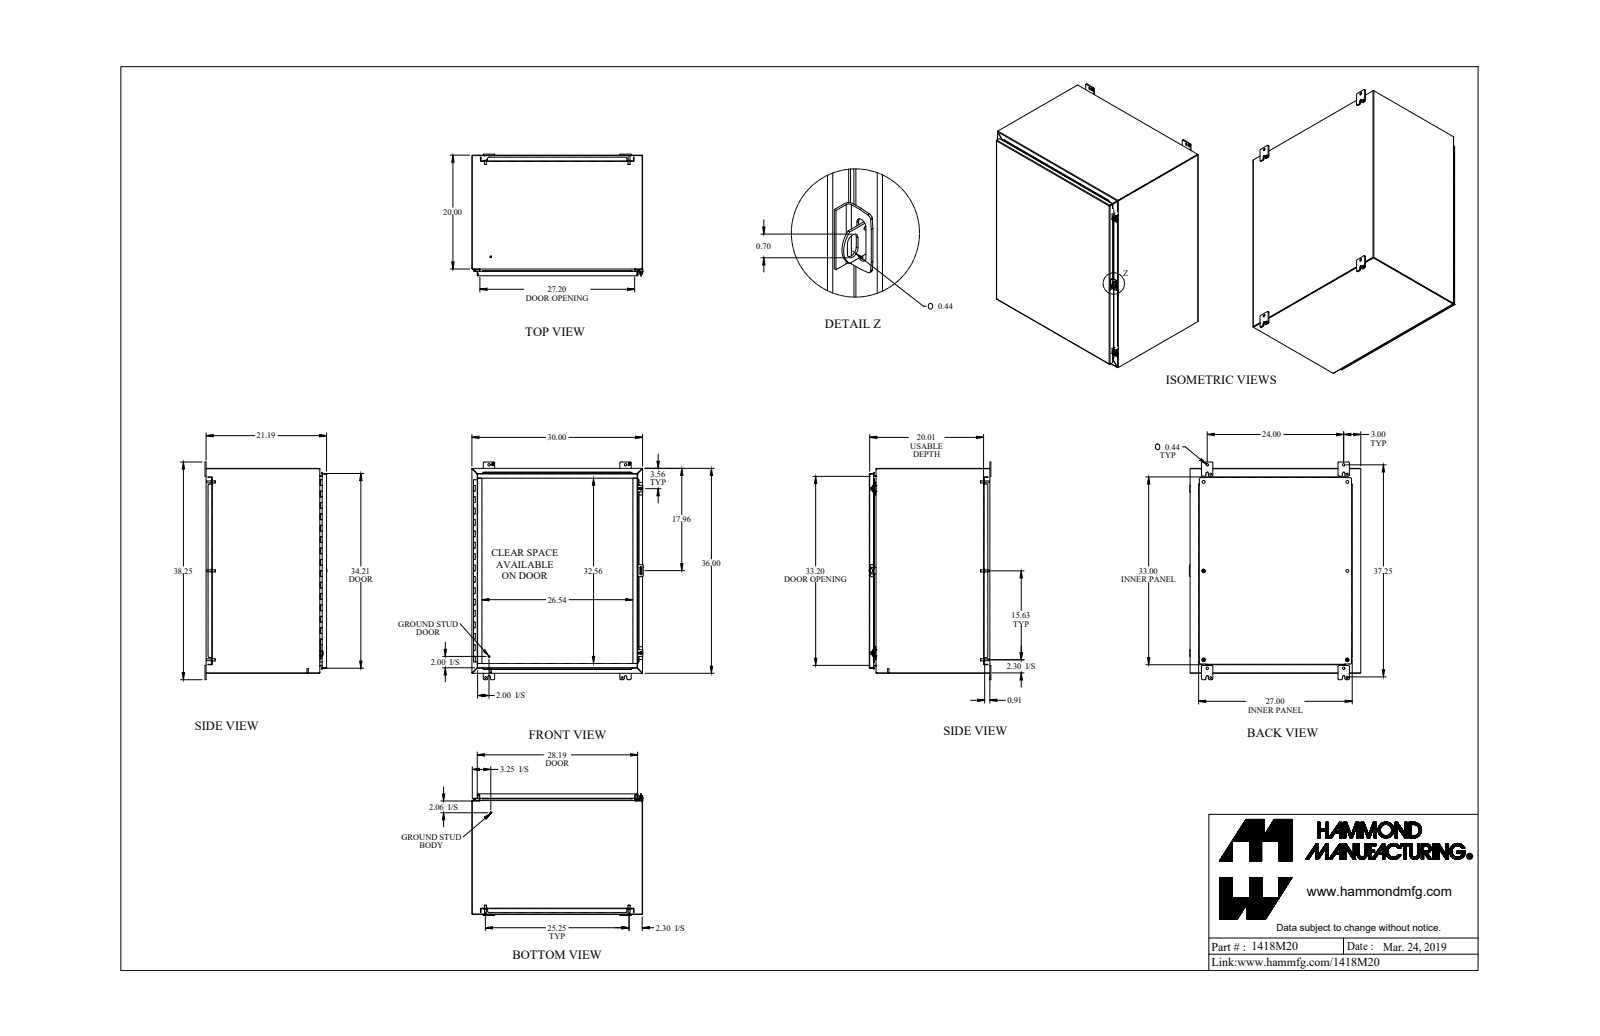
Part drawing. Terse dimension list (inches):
name: 1418M20_Default
written by: SolidWorks 2019 (CONFIG_CONTROL_DESIGN)
unit: in
bodies: 49 solids, 1431 faces (837 planar, 502 cylindrical, 92 other)
size: 38.25 × 30.125 × 21.437
volume: 500.7 in³; area: 13 184 in²
holes: 6× ⌀0.5, 4× ⌀0.307, 4× ⌀0.313, 4× ⌀0.437, 4× ⌀0.445, 2× ⌀0.213, 2× ⌀0.265, 2× ⌀0.375, 1× ⌀0.125, 1× ⌀0.187
bosses: 6× ⌀0.65, 6× ⌀0.375, 6× ⌀0.33, 4× ⌀1, 2× ⌀0.5, 2× ⌀0.39, 2× ⌀0.281, 2× ⌀0.25
rounds: 36× R0.188, 22× R0.036, 22× R0.108, 20× R0.25, 13× R0.048, 13× R0.143, 12× R0.116, 8× R0.04
face distances: 0.072, 21.113, 29.928, 35.928, 21.041, 21.185, 0.095, 0.937, 1.009, 20.081
hole spacings: 25.25, 15.625, 24, 29.694, 43.059, 27.401, 31.25, 31.25
